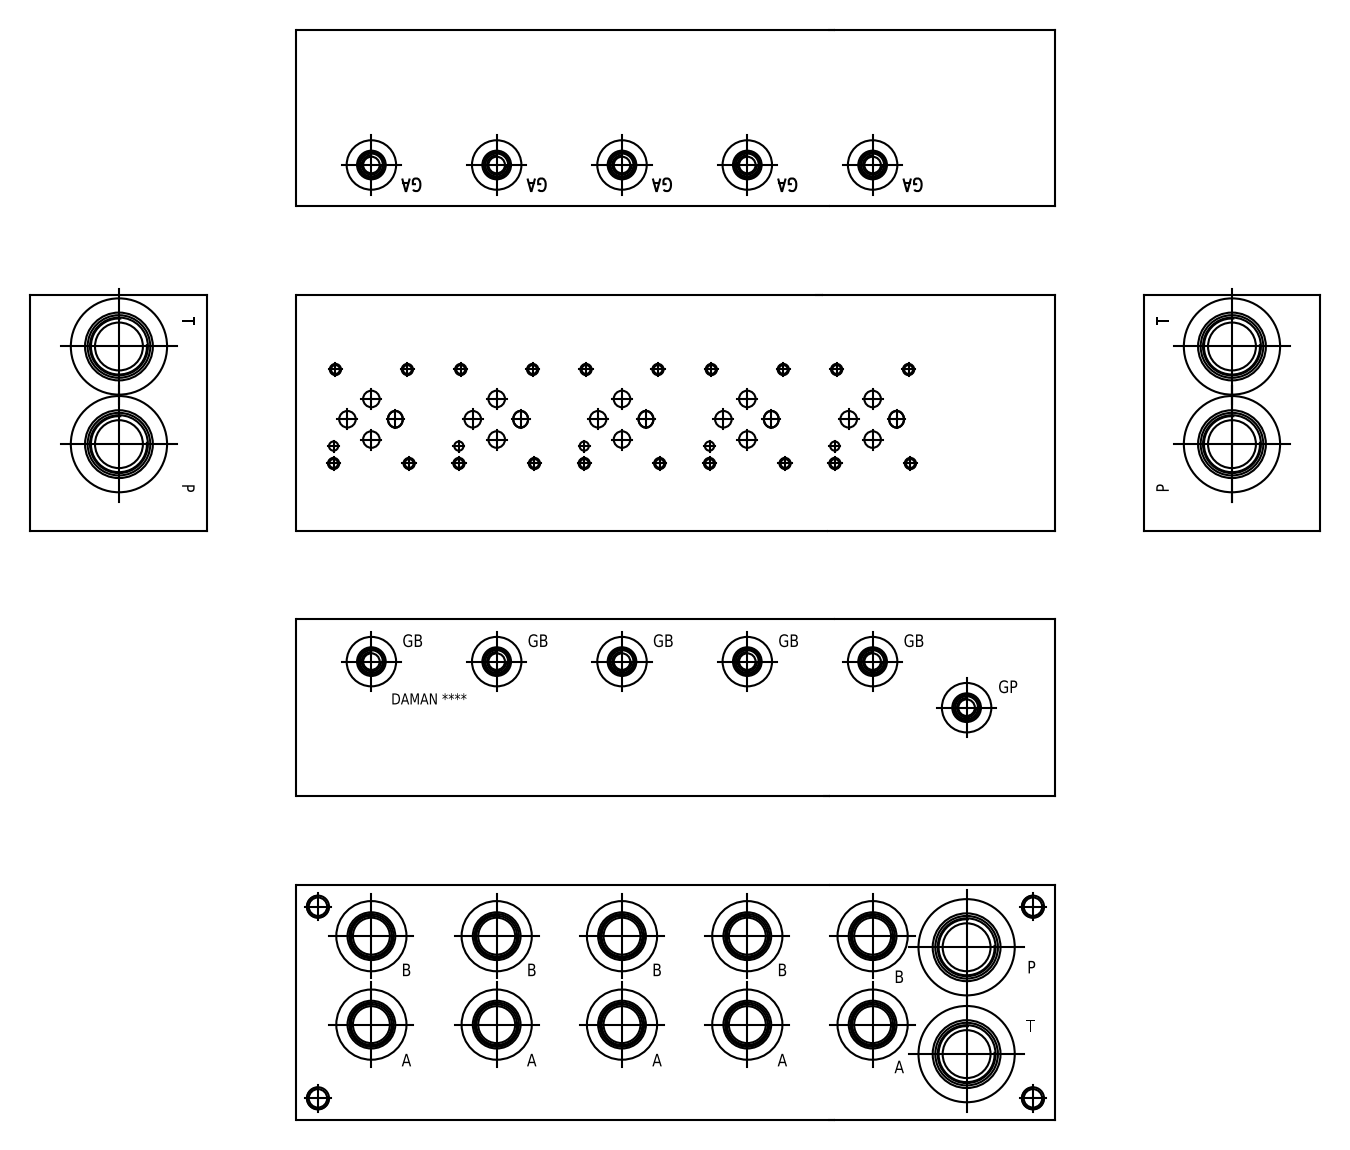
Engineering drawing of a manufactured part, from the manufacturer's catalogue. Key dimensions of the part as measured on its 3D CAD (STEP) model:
Part name (STEP PRODUCT): Part_DD03PB052S_3D
STEP written by: Autodesk Inventor 2019 (AUTOMOTIVE_DESIGN)
Units: millimetres
Bodies: 1 solid, 1514 faces (717 planar, 195 cylindrical, 602 other)
Overall size (bounding box): 327.02 × 101.6 × 76.2
Volume: 2 327 000 mm³ · Surface area: 175 248 mm²
Round holes (diameter × count): ⌀7.14 ×25, ⌀3.78 ×20, ⌀4.83 ×20, ⌀9.88 ×11, ⌀11.13 ×11, ⌀21.29 ×11, ⌀15.88 ×10, ⌀17.5 ×10, ⌀19.05 ×10, ⌀19.25 ×10, ⌀30.63 ×10, ⌀3.96 ×5
Main face-to-face distances: 76.2, 101.6, 0.79, 75.41, 327.02, 100.81, 326.23, 326.24, 325.45, 0.78
Hole centre spacings: 107.95, 53.97, 53.98, 40.5, 51.45, 161.92, 161.93, 22.05
